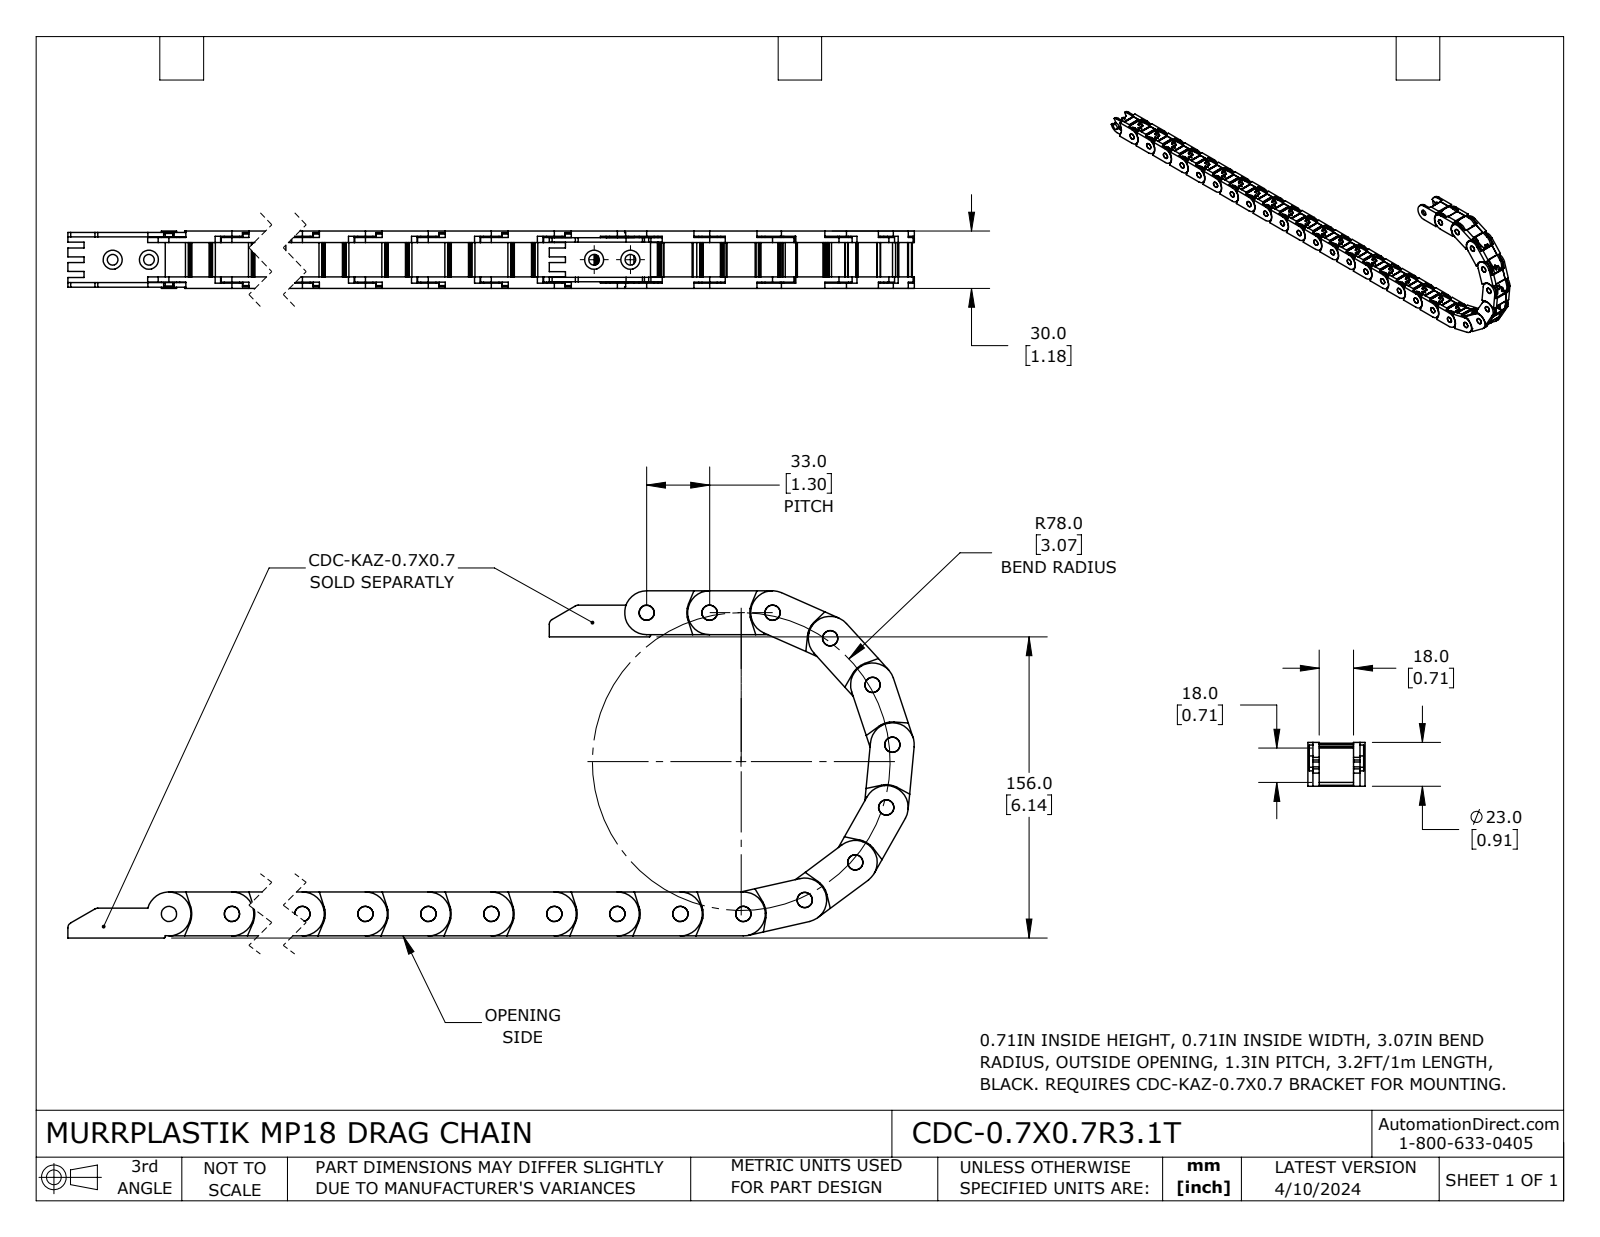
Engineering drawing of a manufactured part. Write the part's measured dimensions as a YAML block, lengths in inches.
part_name: "CDC-0.7X0.7R3.1T"
step_written_by: "SolidWorks 2023 (CONFIG_CONTROL_DESIGN)"
units: inches
bodies: {solids: 29, faces: 2639, planar: 1479, cylindrical: 1160, other: 0}
overall_size: [29.95, 7.115, 1.181]
volume: 15.58
surface_area: 310.9
round_holes:
  - {diameter: 0.315, count: 29}
round_bosses_or_shafts:
  - {diameter: 0.315, count: 1}
partial_cylinders:
  - {radius: 0.02, count: 116}
  - {radius: 0.059, count: 116}
  - {radius: 0.008, count: 58}
  - {radius: 0.012, count: 58}
  - {radius: 0.453, count: 30}
  - {radius: 0.47, count: 30}
  - {radius: 0.197, count: 29}
  - {radius: 0.215, count: 29}
face_to_face_distances: [0.945, 0.236, 0.106, 0.13, 1.181, 1.051, 0.815, 0.709, 1.075, 0.024]
hole_center_spacings: [1.299, 2.598, 3.898, 5.197, 6.496, 7.795, 9.094, 10.394]
